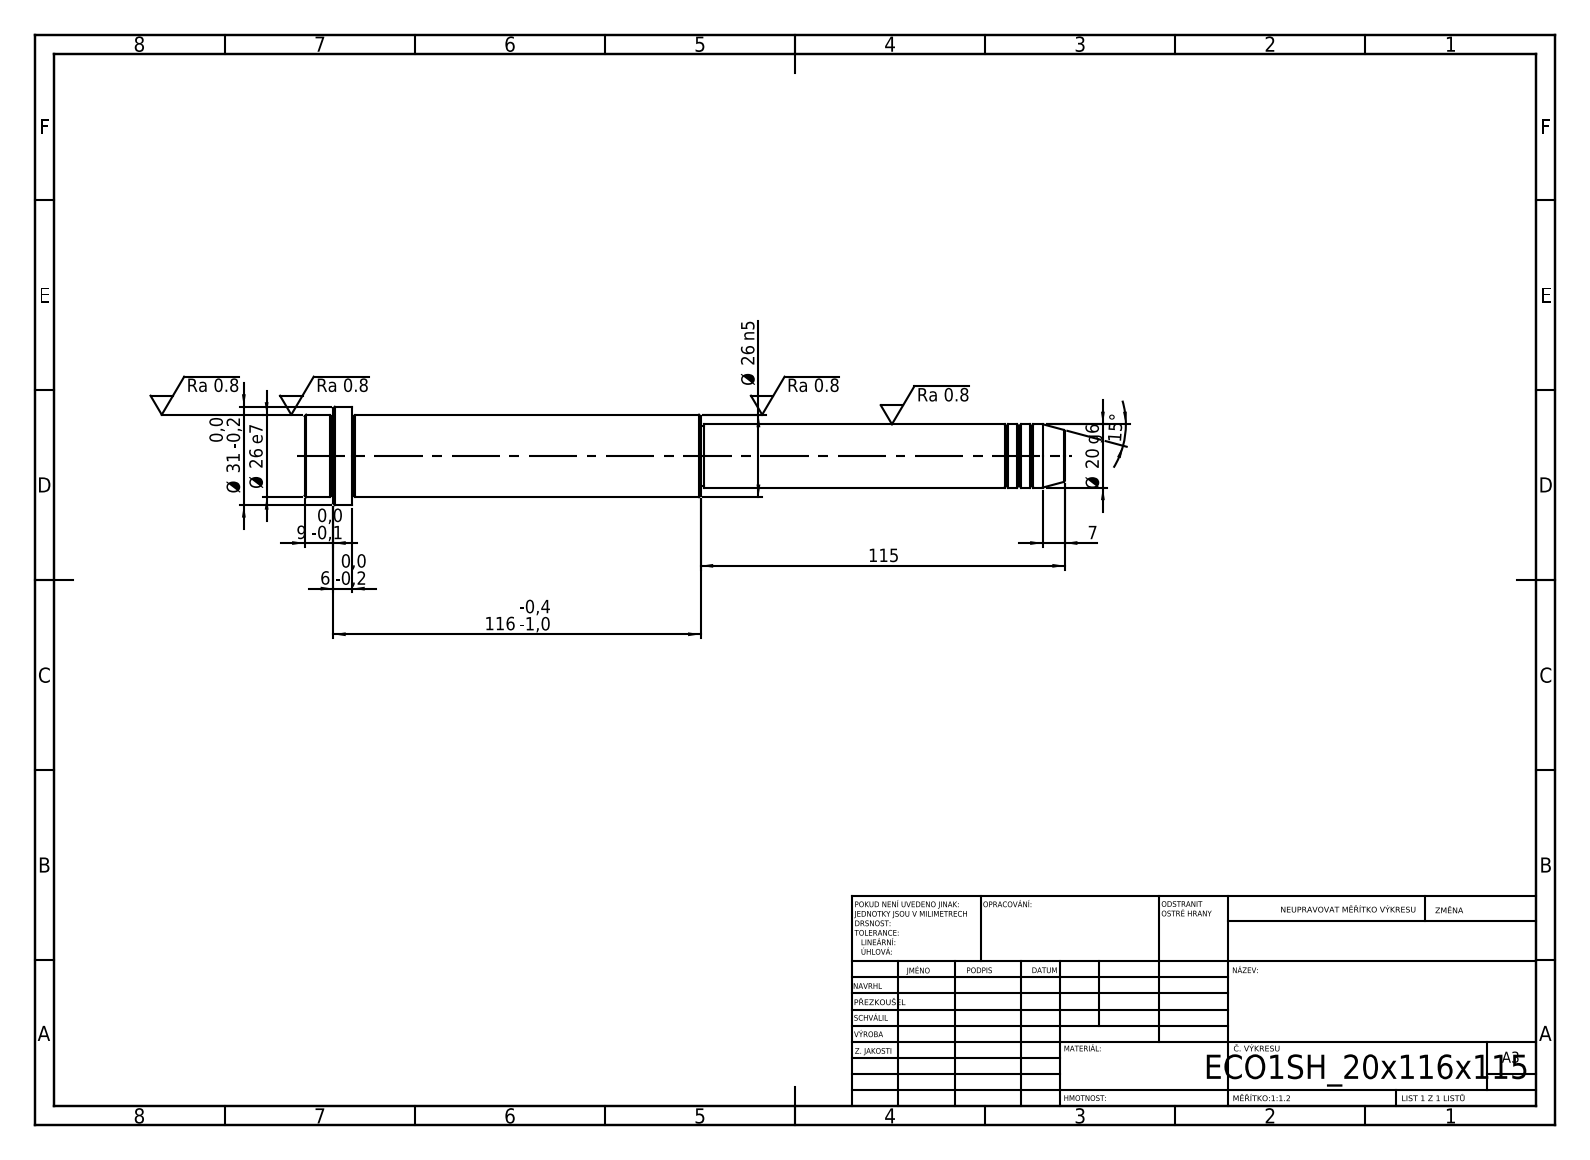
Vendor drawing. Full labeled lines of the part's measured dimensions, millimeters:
STEP written by: SolidWorks 2019 (CONFIG_CONTROL_DESIGN)
Units: millimetres
Bodies: 1 solid, 52 faces (6 planar, 16 cylindrical, 30 other)
Overall size (bounding box): 240 × 31 × 31
Volume: 103 251 mm³ · Surface area: 19 066 mm²
Round bosses / shafts (diameter × count): ⌀31 ×1, ⌀26 ×1, ⌀20 ×1, ⌀19 ×1
Main face-to-face distances: 15, 110, 125, 115, 225, 240, 231, 116, 6, 9
